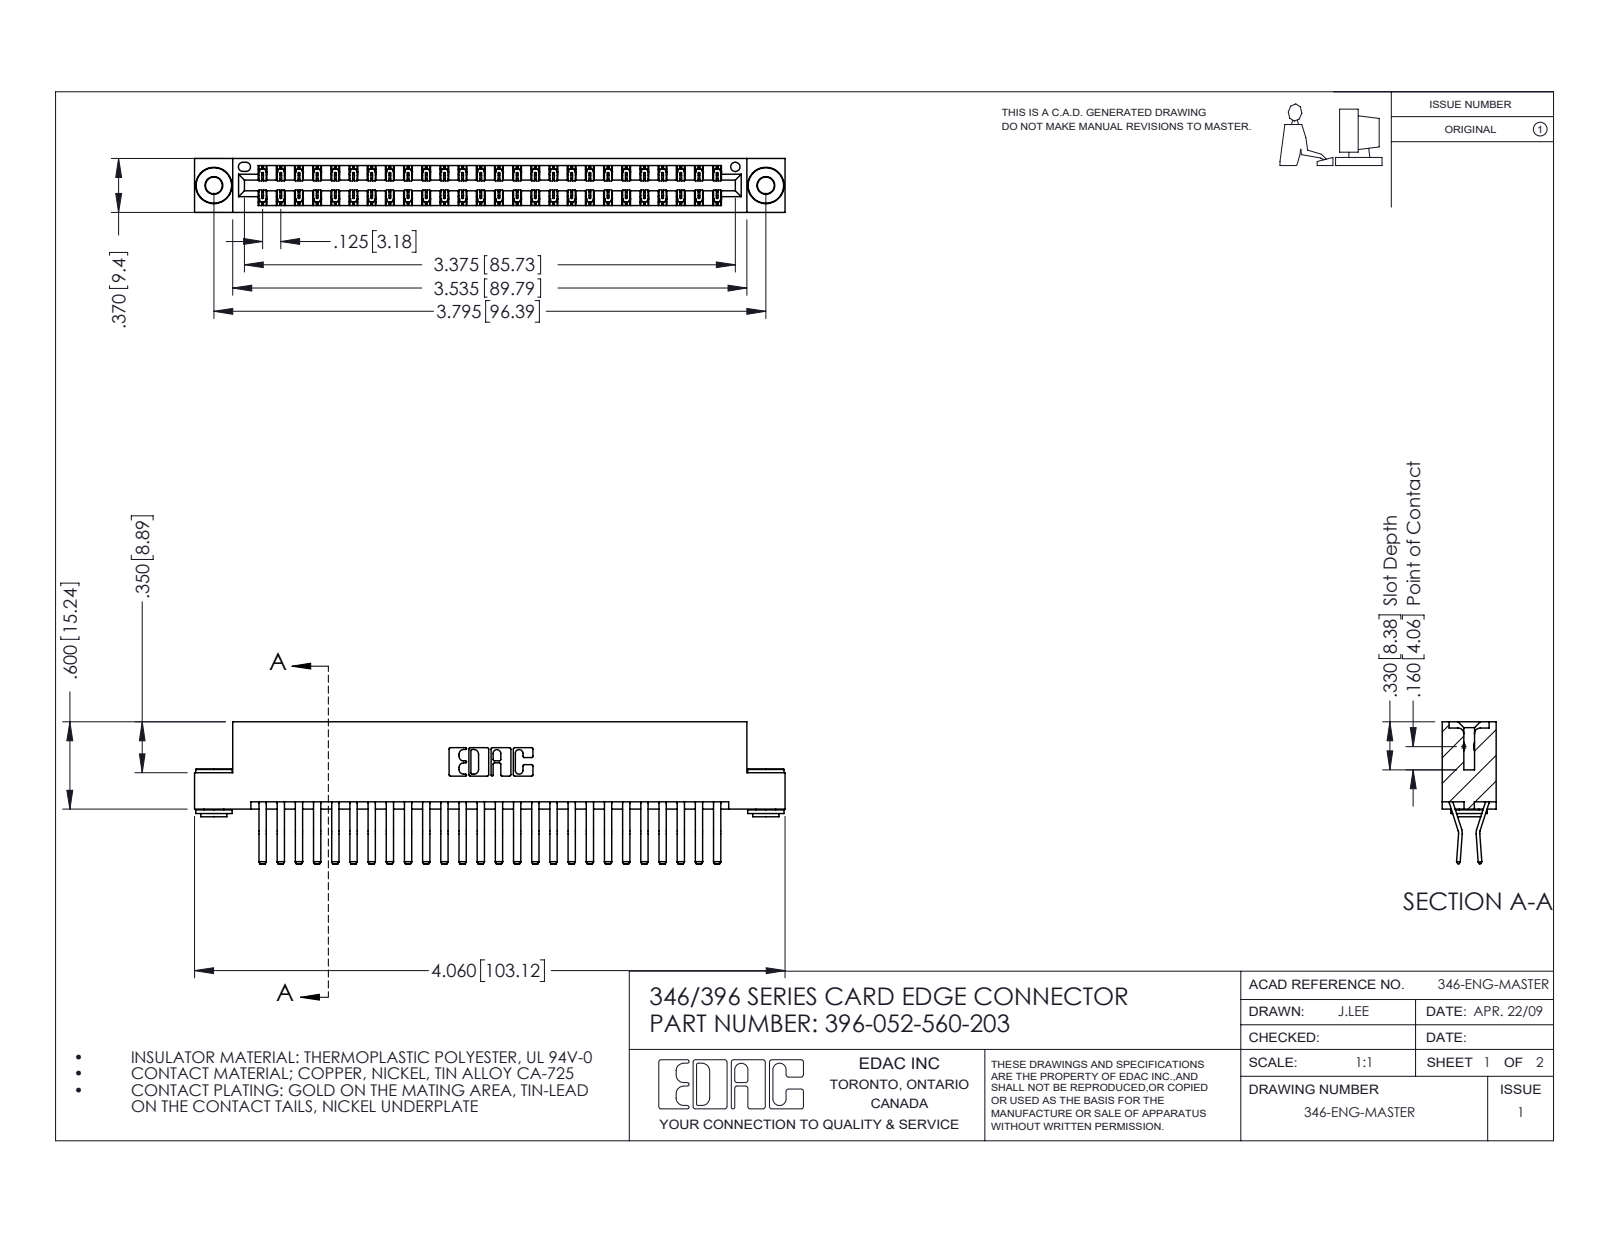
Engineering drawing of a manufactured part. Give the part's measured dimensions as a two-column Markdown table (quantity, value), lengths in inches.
| quantity | value |
| --- | --- |
| part name | 345-250-002_345-250-002-102; 396-052-560-203; 345-292-001_560 Tail; 346 Part_Flush Mounting Lugs - 0.156 Dia-TH |
| STEP written by | SolidWorks 2016 (CONFIG_CONTROL_DESIGN) |
| units | inches |
| bodies | 55 solids, 2968 faces (1906 planar, 1054 cylindrical, 8 other) |
| overall size | 4.06 × 0.975 × 0.37 |
| volume | 0.628 in³ |
| surface area | 23.28 in² |
| round holes (diameter × count) | 0.116 × 2, 0.156 × 2, 0.064 × 1 |
| round bosses / shafts (diameter × count) | 0.25 × 2, 0.18 × 2, 0.136 × 2 |
| partial cylindrical surfaces (radius × count) | 0.006 × 78, 0.01 × 22, 0.007 × 6, 0.031 × 6, 0.026 × 3, 0.01 × 2, 0.014 × 2, 0.022 × 2 |
| main face-to-face distances | 0.048, 0.322, 0.25, 0.37, 0.025, 0.072, 0.298, 0.275, 0.148, 0.222 |
| hole center spacings | 0.246, 3.587, 3.795 |
